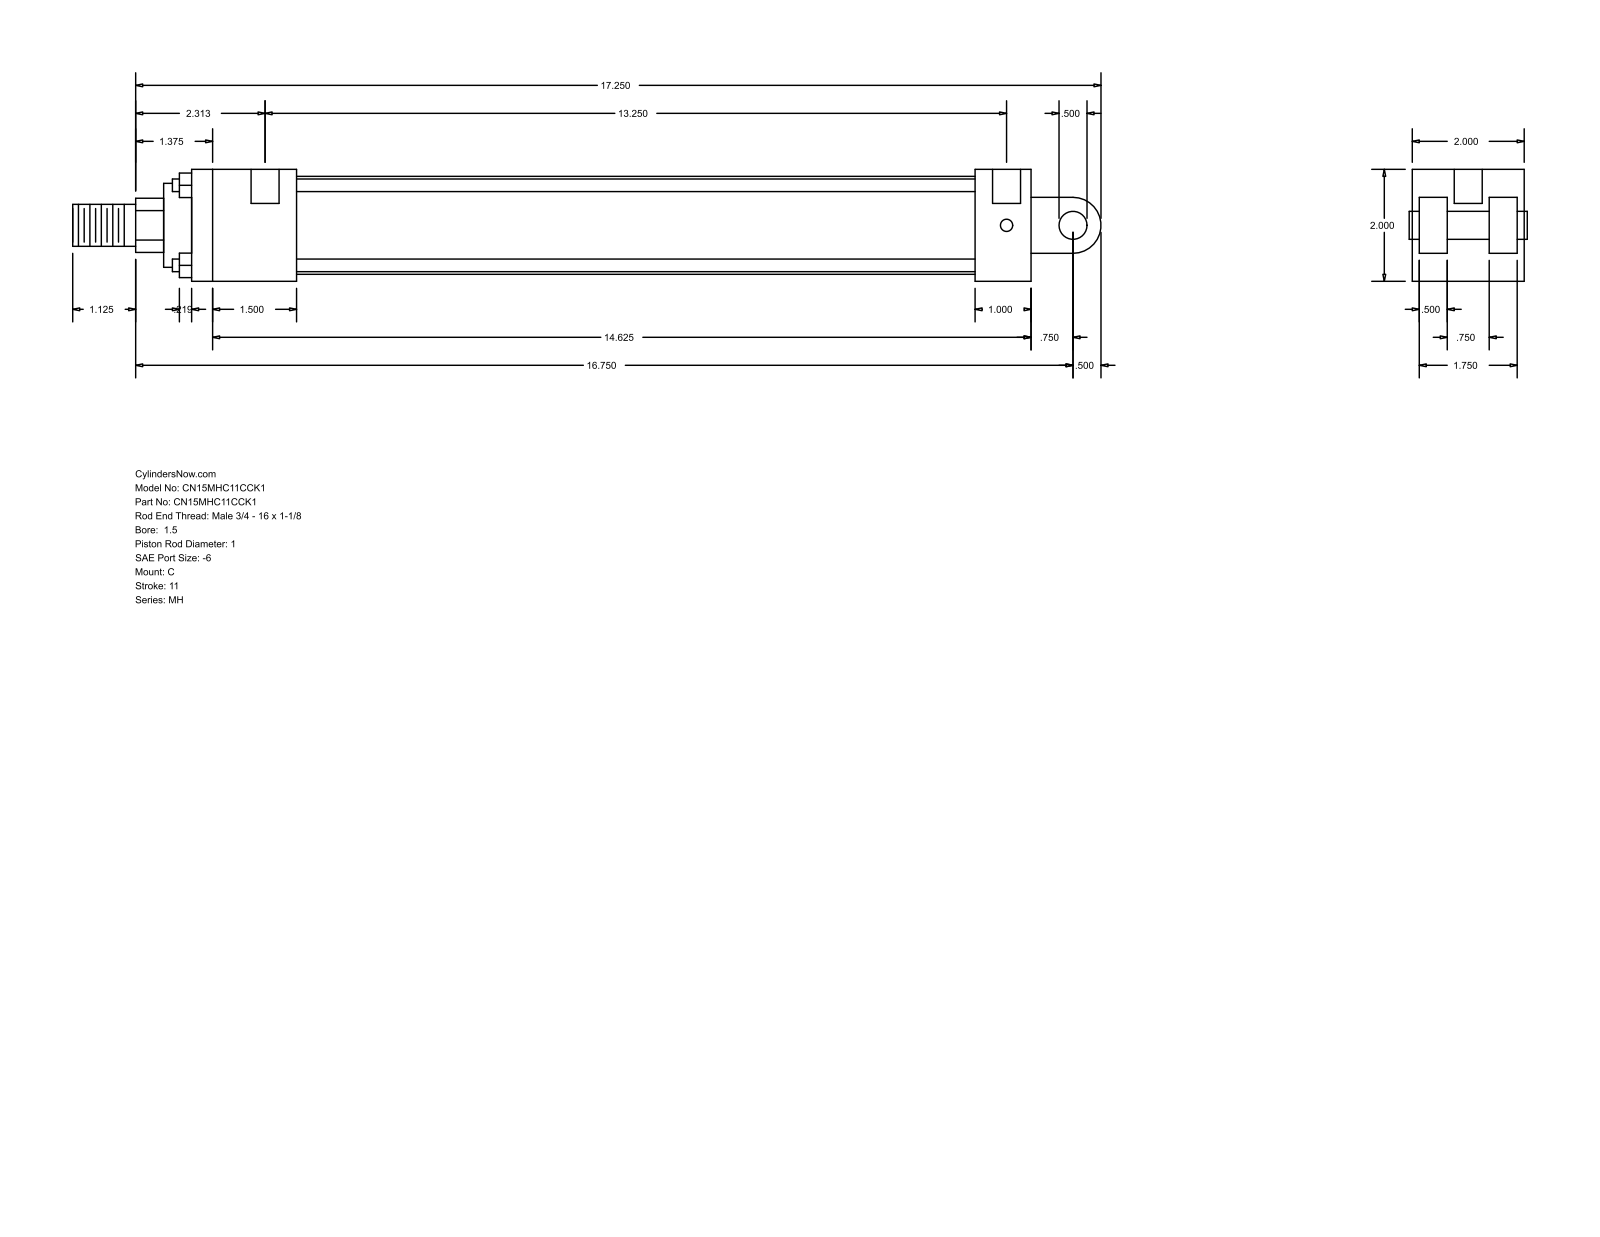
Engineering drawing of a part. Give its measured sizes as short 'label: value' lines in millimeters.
name: MH_C__0150_1
written by: GSSL Pune (CONFIG_CONTROL_DESIGN)
unit: mm
bodies: 0 solids, 99 faces (70 planar, 29 cylindrical, 0 other)
size: 466.73 × 50.8 × 50.8
holes: 4× ⌀5.56, 2× ⌀12.7
bosses: 4× ⌀5.71, 1× ⌀44.45, 1× ⌀38.1, 1× ⌀25.4, 1× ⌀19.05, 1× ⌀12.7
rounds: 1× R12.29, 1× R12.7
face distances: 50.8, 12.7, 47.63, 25.4, 3.17, 15.87, 34.93, 31.76, 381, 38.1
hole spacings: 339.73, 3.18, 336.55
